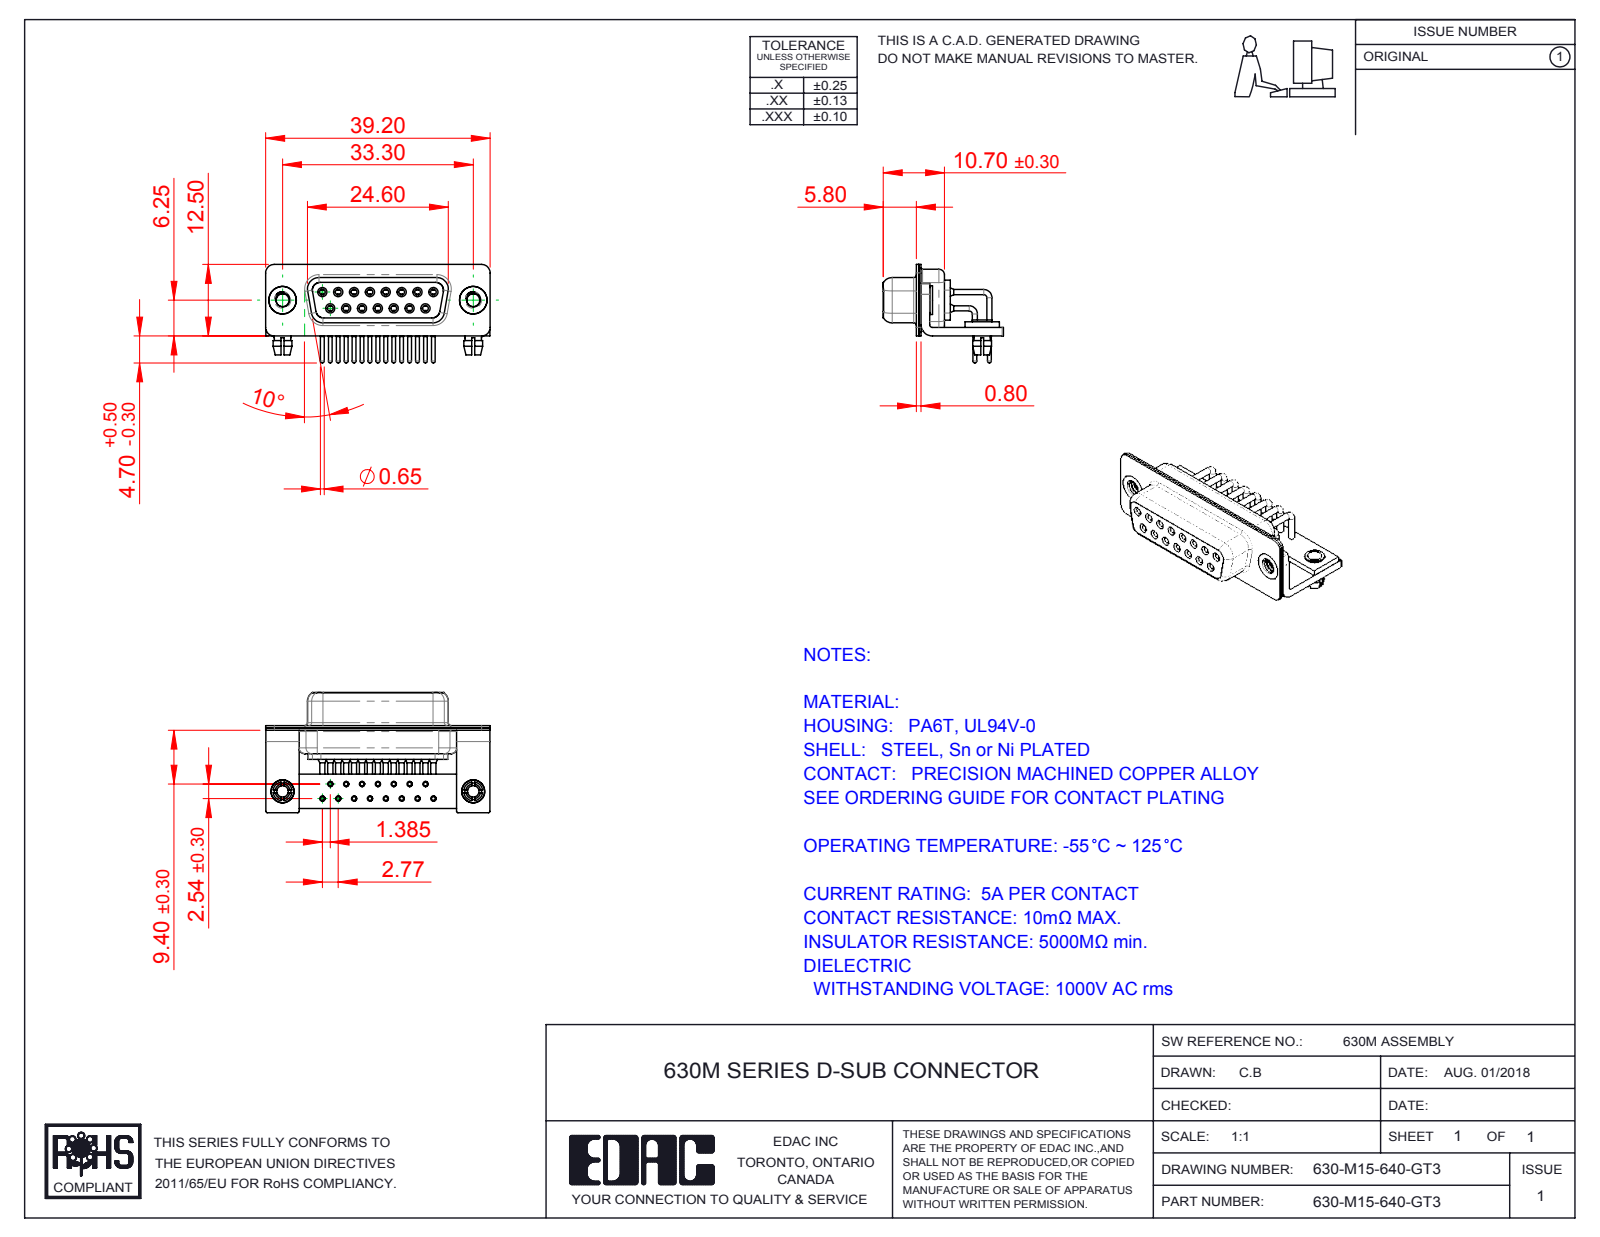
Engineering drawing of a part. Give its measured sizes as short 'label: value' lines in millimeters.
name: 630M Shell Rear_15 Contacts; 630M Contact Row 2; 630-M15-640-GT3; 630M Shell Front_15 Contacts (+6 more)
written by: SolidWorks 2016 (CONFIG_CONTROL_DESIGN)
unit: mm
bodies: 25 solids, 1246 faces (366 planar, 566 cylindrical, 314 other)
size: 39.2 × 21 × 17.2
volume: 3 090 mm³; area: 7 958 mm²
holes: 17× ⌀2, 15× ⌀0.9, 15× ⌀1, 15× ⌀1.1, 15× ⌀1.7, 15× ⌀1.8, 2× ⌀2.26, 2× ⌀2.5, 2× ⌀3.2, 2× ⌀4, 2× ⌀4.8
bosses: 27× ⌀0.9, 15× ⌀1.6, 15× ⌀1.5, 15× ⌀0.65, 2× ⌀5, 2× ⌀4.9, 2× ⌀4, 2× ⌀3.4
rounds: 16× R0.25, 16× R1.5, 13× R2, 8× R1.35, 8× R1.6, 5× R0.5, 4× R0.6, 4× R0.65
face distances: 0.4, 0.8, 2.3, 1.5, 9.35, 1.9, 1, 1.45, 8.95, 0.85
hole spacings: 2.77, 5.54, 8.31, 3.16, 4.87, 11.08, 2.89, 7.37
